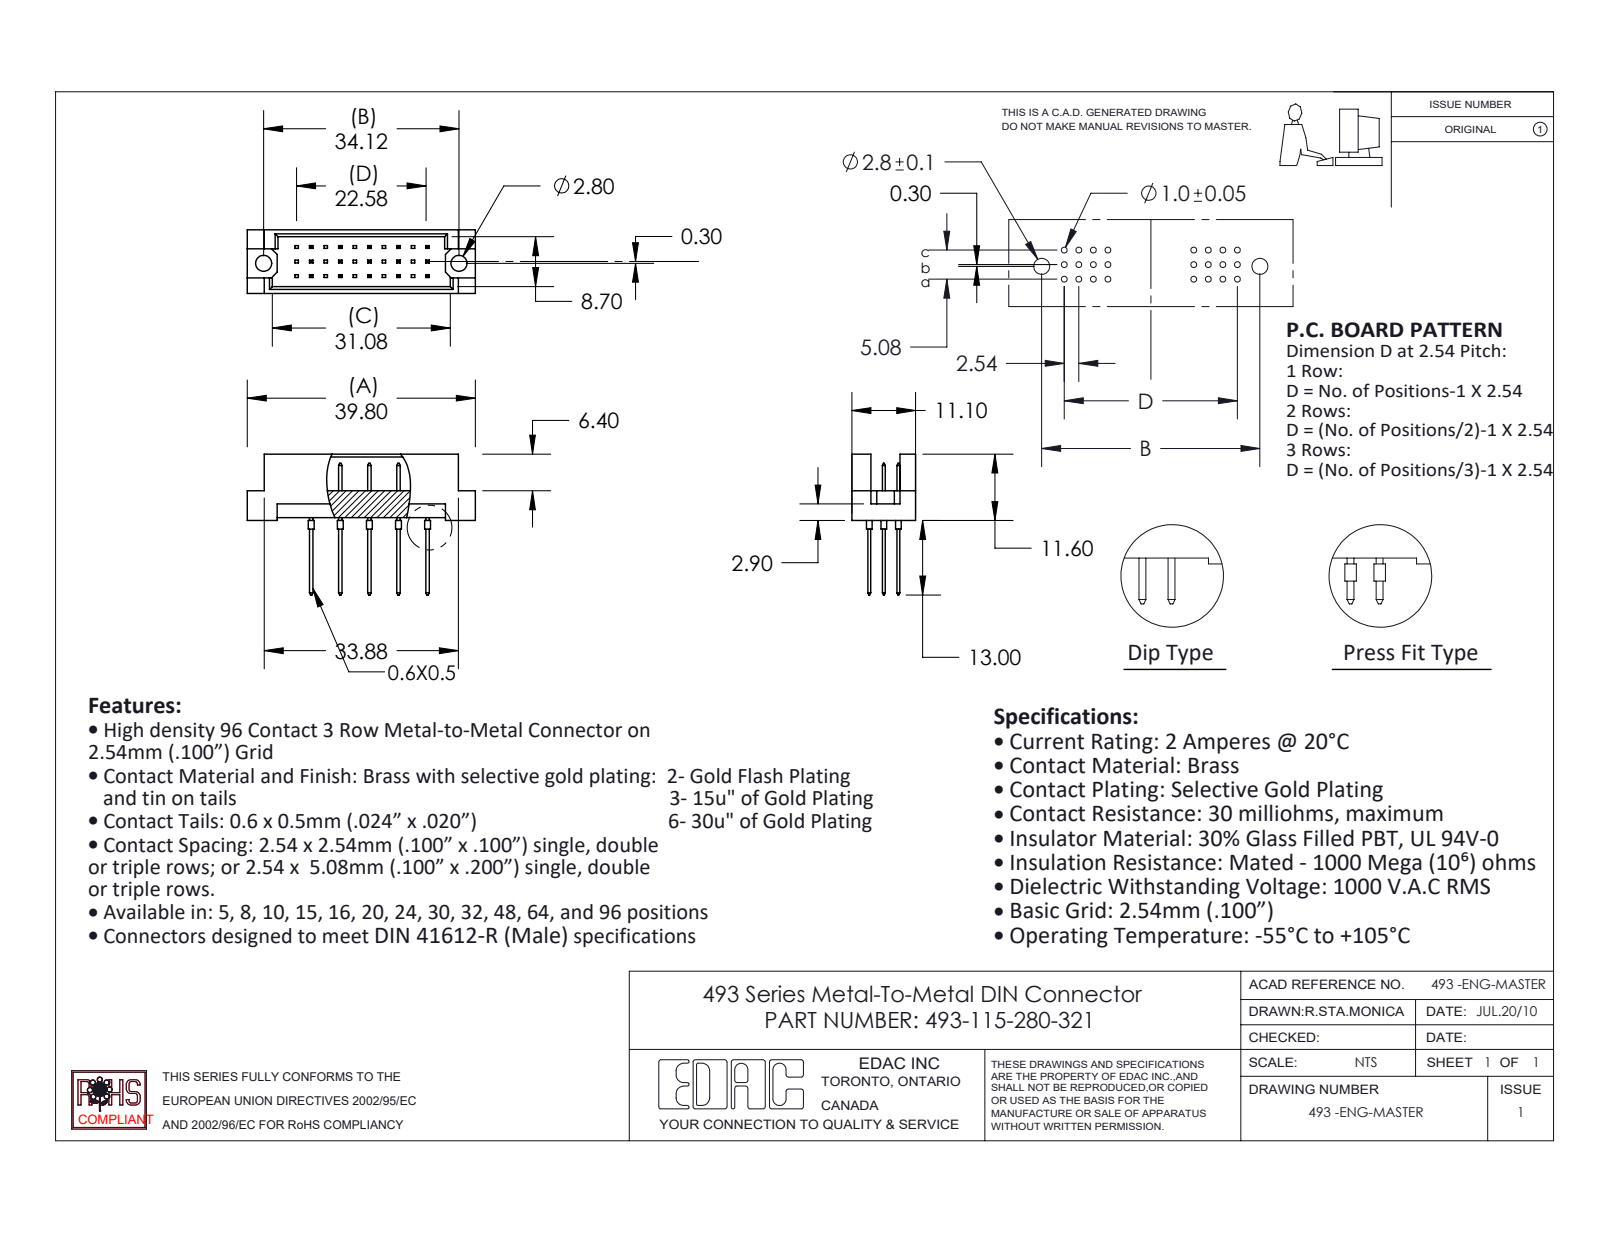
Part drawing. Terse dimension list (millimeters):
name: 493-115-280-321; 493-290_80; 493 Part_30
written by: SolidWorks 2020 (CONFIG_CONTROL_DESIGN)
unit: mm
bodies: 16 solids, 502 faces (468 planar, 34 cylindrical, 0 other)
size: 39.8 × 24.6 × 11.1
volume: 2 486 mm³; area: 3 527 mm²
holes: 2× ⌀2.8
bosses: 15× ⌀1
face distances: 5.08, 1.2, 9.9, 11.1, 0.5, 2.54, 8.7, 4.7, 10.16, 0.6
hole spacings: 34.12
